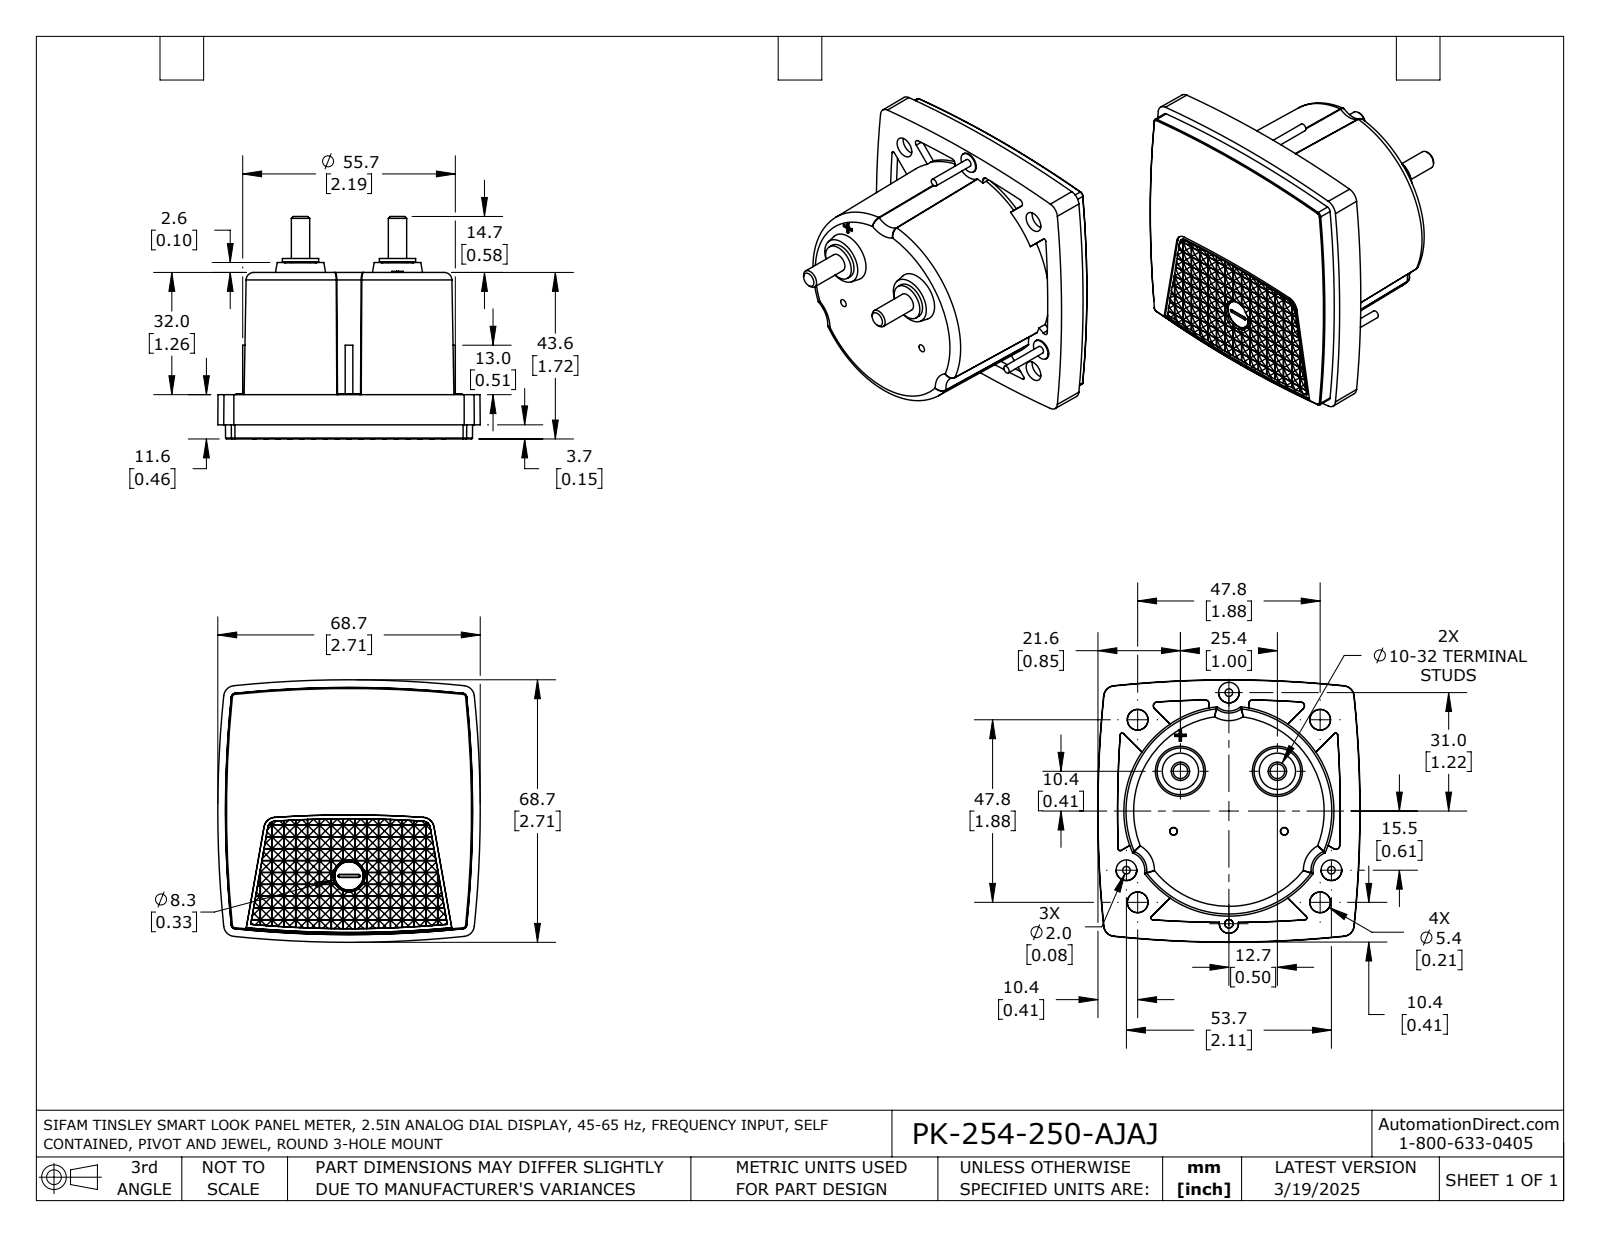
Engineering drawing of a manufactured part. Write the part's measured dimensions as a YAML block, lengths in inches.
part_name: "PK-254-250-AJAJ"
step_written_by: "SolidWorks 2021 (AUTOMOTIVE_DESIGN)"
units: inches
bodies: {solids: 1, faces: 1550, planar: 1165, cylindrical: 265, other: 120}
overall_size: [2.706, 2.706, 2.297]
volume: 7.594
surface_area: 30.41
round_bosses_or_shafts:
  - {diameter: 0.213, count: 3}
  - {diameter: 0.079, count: 3}
  - {diameter: 0.374, count: 2}
  - {diameter: 0.189, count: 2}
  - {diameter: 0.215, count: 1}
partial_cylinders:
  - {radius: 0.167, count: 2}
  - {radius: 1.083, count: 1}
face_to_face_distances: [1.717, 1.26, 0.457, 0.024, 0.087, 0.096, 0.311, 0.12, 0.072, 1.346]
